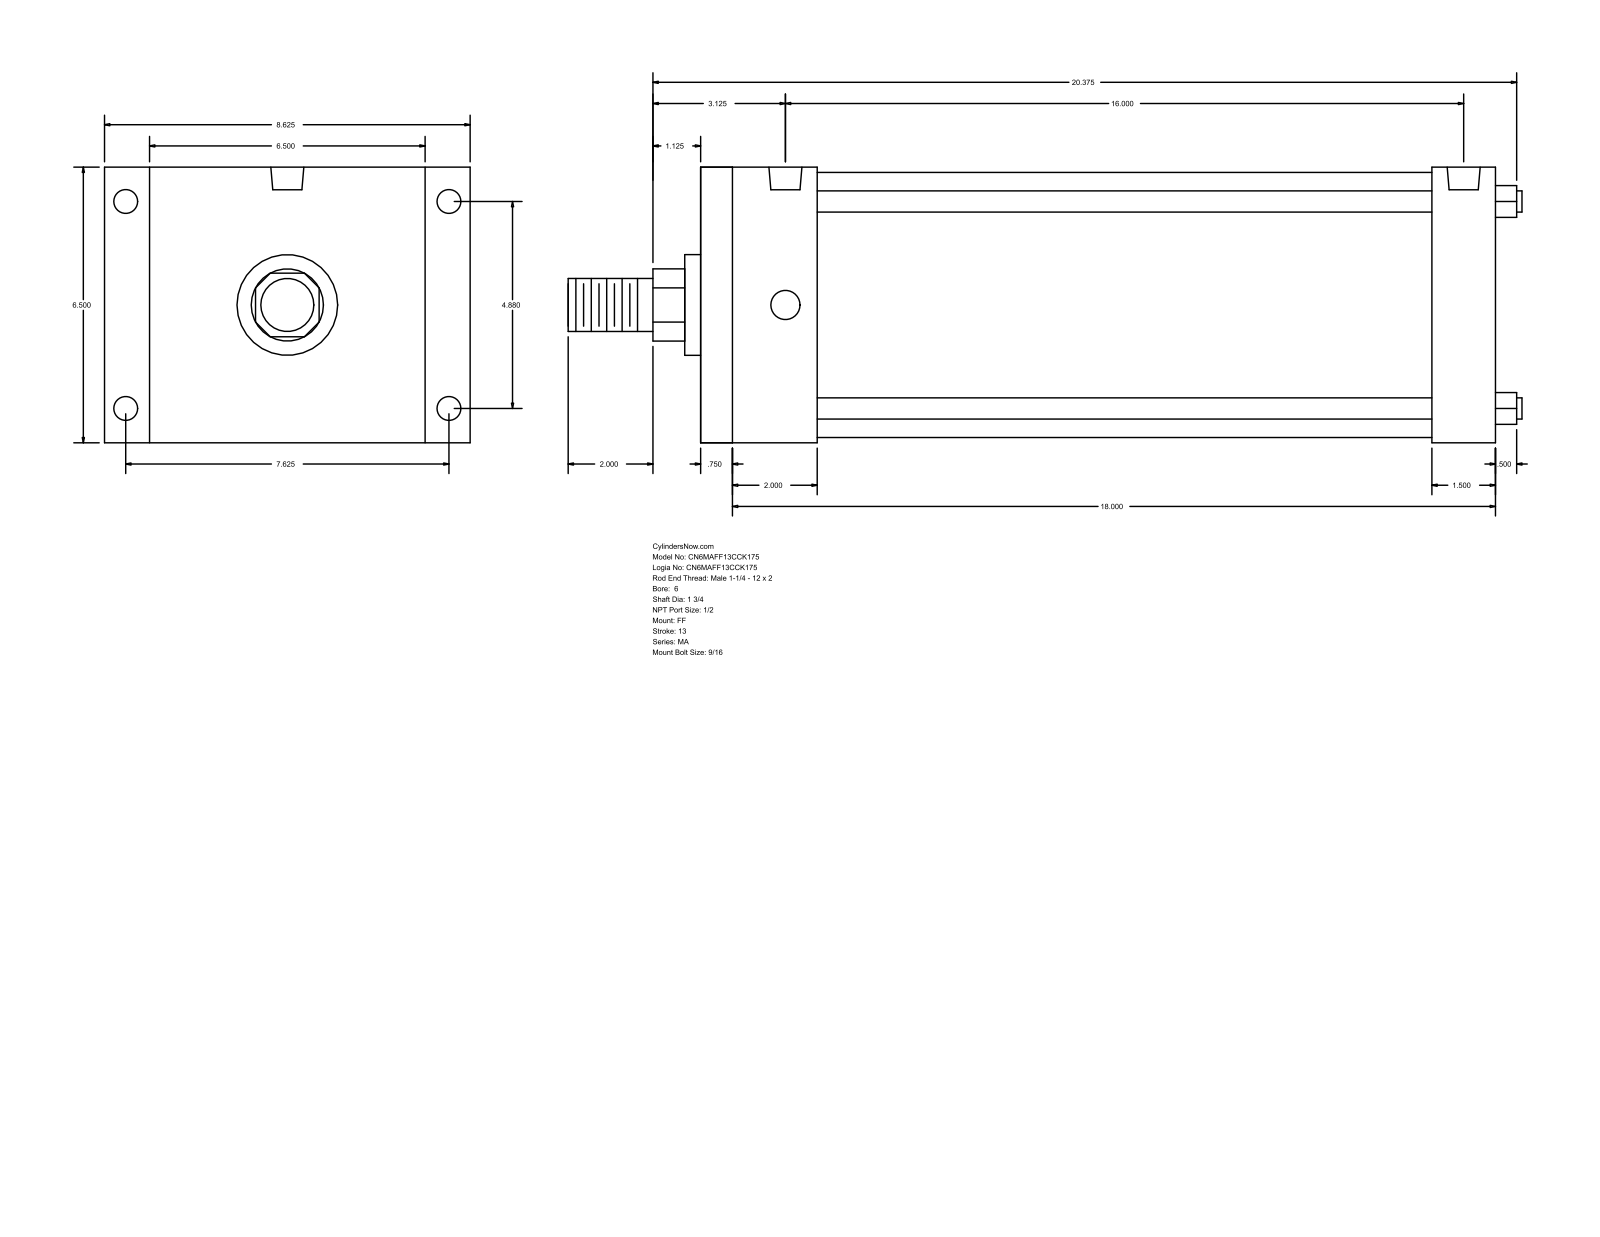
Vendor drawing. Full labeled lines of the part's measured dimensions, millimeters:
Part name (STEP PRODUCT): MA_FF__0600_1.75
STEP written by: GSSL Pune (CONFIG_CONTROL_DESIGN)
Units: millimetres
Bodies: 0 solids, 92 faces (64 planar, 28 cylindrical, 0 other)
Overall size (bounding box): 571.5 × 219.07 × 165.1
Round holes (diameter × count): ⌀14.29 ×4, ⌀17.46 ×4, ⌀19.77 ×2
Round bosses / shafts (diameter × count): ⌀12.7 ×4, ⌀158.75 ×1, ⌀60.33 ×1, ⌀44.45 ×1, ⌀31.75 ×1
Partial cylindrical surfaces — rounded edges, fillets, slot ends (radius × count): R21.63 ×1
Main face-to-face distances: 165.1, 476.25, 19.05, 457.2, 69.85, 50.8, 406.4, 438.16, 419.11, 368.31
Hole centre spacings: 123.96, 193.68, 229.95, 406.39
